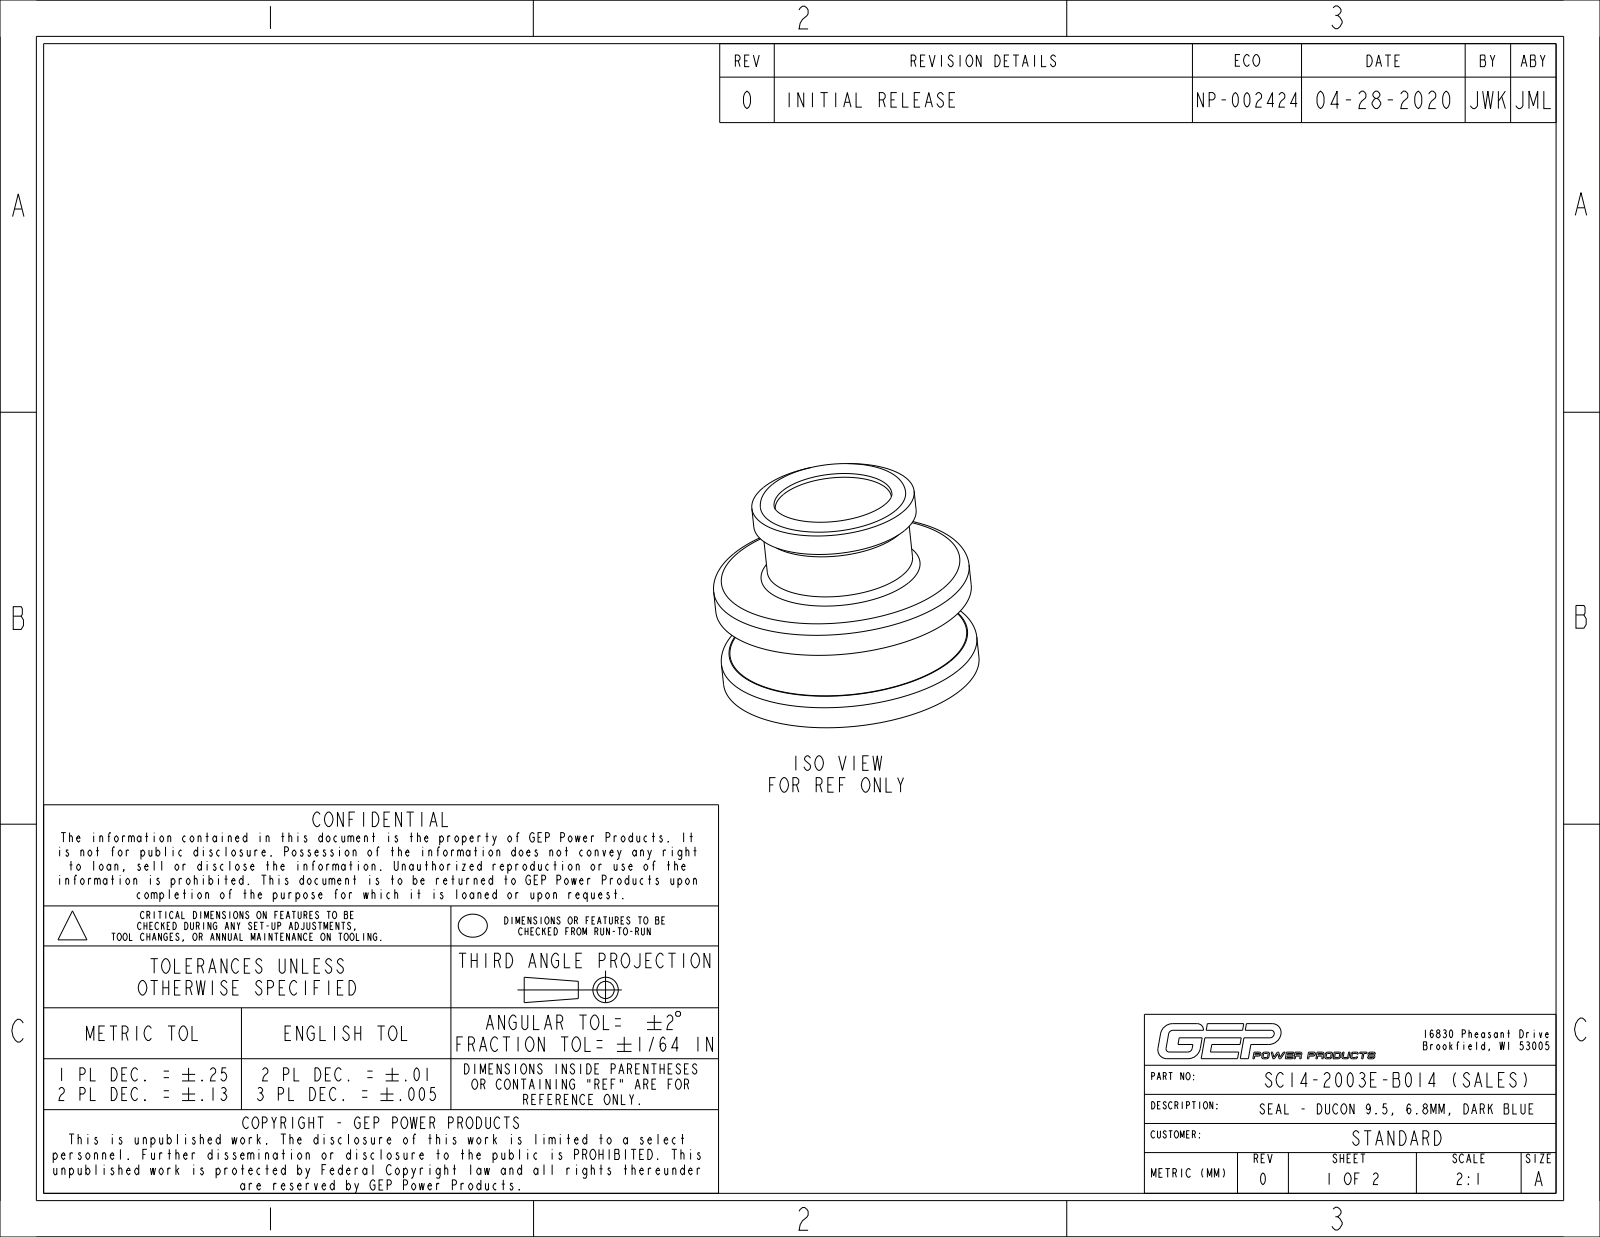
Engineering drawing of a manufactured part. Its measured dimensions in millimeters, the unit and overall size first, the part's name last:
Units: millimetres
Overall size (bounding box): 14.95 × 14.95 × 12.1
Round holes (diameter × count): ⌀6.8 ×1
Round bosses / shafts (diameter × count): ⌀14.95 ×1, ⌀9.5 ×1, ⌀8.5 ×1
Main face-to-face distances: 6.5, 1.8, 4.7, 11.1, 6.4, 4.6, 9.9, 5.2, 3.4, 1.2
Volume: 802 mm³ · Surface area: 1 078 mm²
Bodies: 1 solid, 87 faces (41 planar, 10 cylindrical, 36 other)
Part name (STEP PRODUCT): PC14-2003E-B014_NCF; SC14-2003E-B014_NCF_ASM
STEP written by: CREO PARAMETRIC BY PTC INC, 2017110 (CONFIG_CONTROL_DESIGN)
